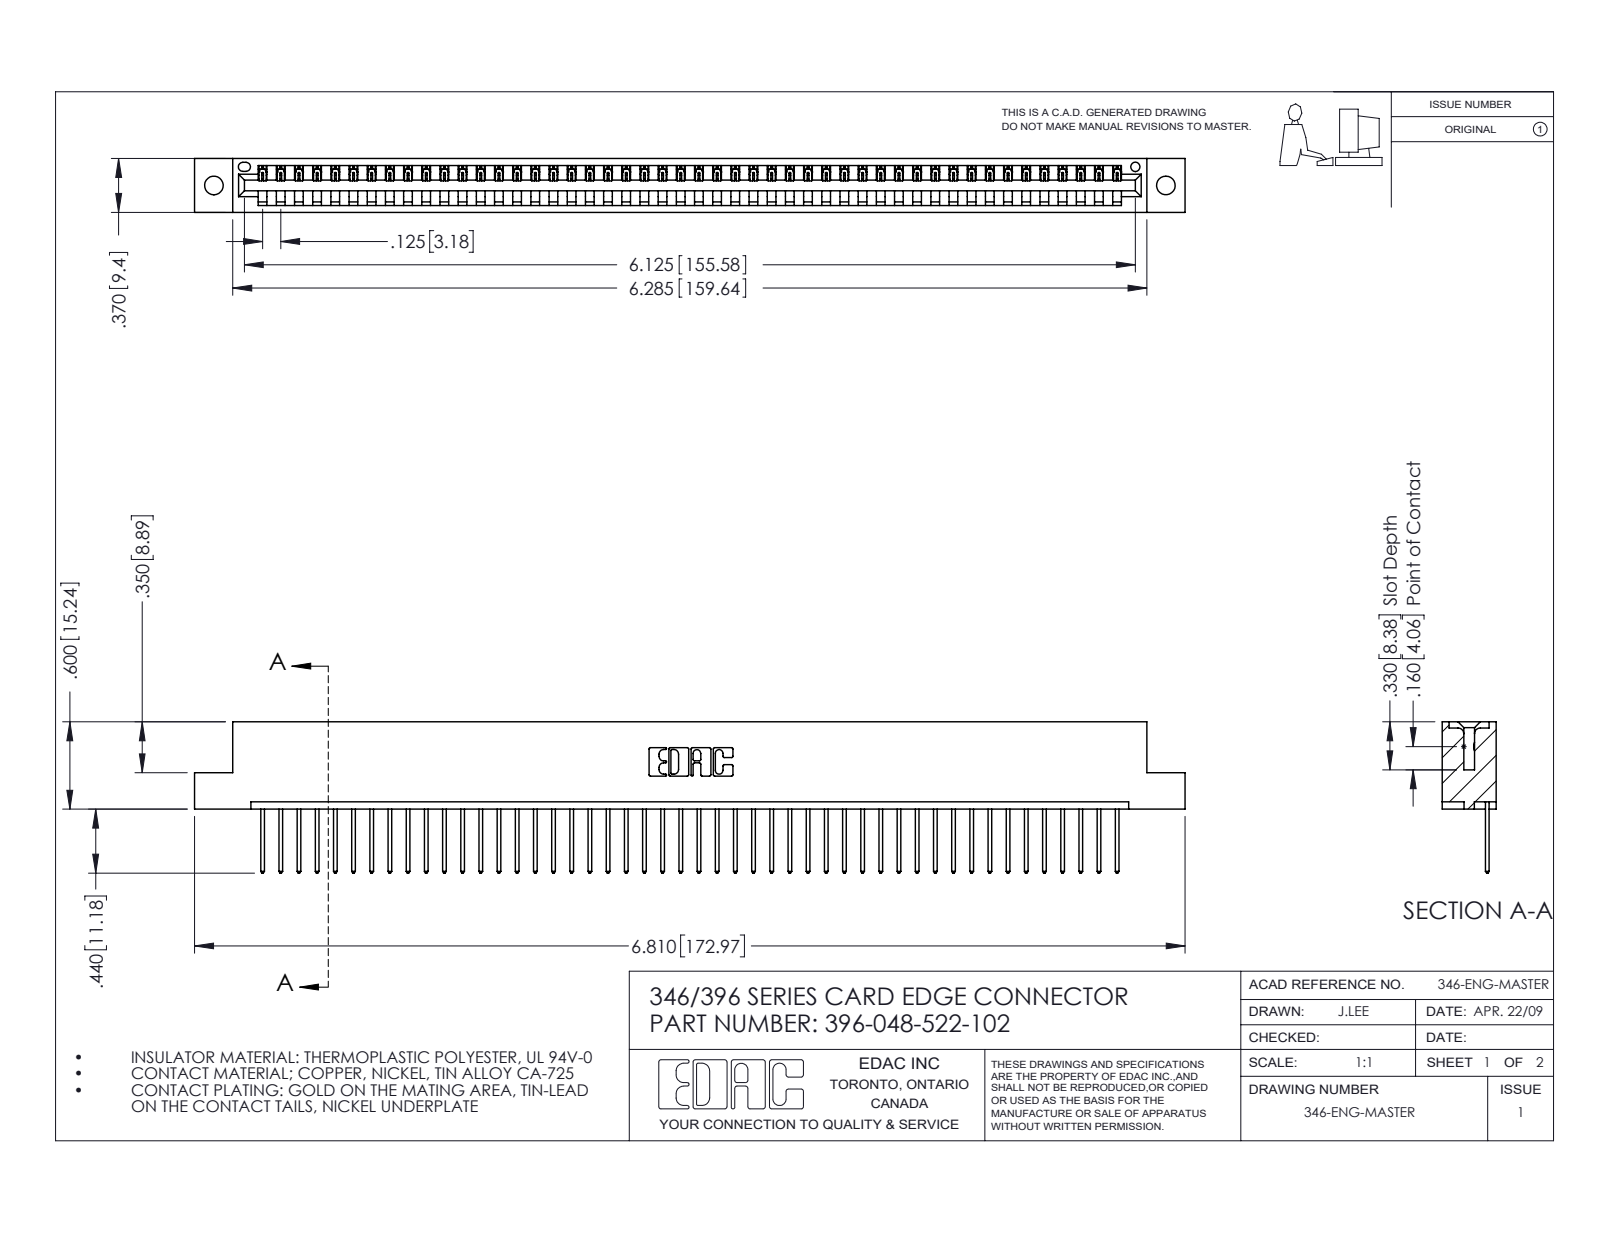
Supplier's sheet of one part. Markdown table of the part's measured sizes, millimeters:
| quantity | value |
| --- | --- |
| part name | 346 Part_Flush Mounting Lugs - 0.128 Dia; 396-048-522-102; 345-292-001_345-293-122 |
| STEP written by | SolidWorks 2016 (CONFIG_CONTROL_DESIGN) |
| units | millimeters |
| bodies | 49 solids, 2906 faces (1996 planar, 910 cylindrical, 0 other) |
| overall size | 173 × 26.4 × 9.4 |
| volume | 16 570 mm³ |
| surface area | 20 680 mm² |
| round holes (diameter × count) | 3.3 × 2, 1.6 × 1 |
| partial cylindrical surfaces (radius × count) | 0.2 × 96, 0.3 × 96, 0.3 × 22, 0.2 × 6, 0.8 × 6, 0.7 × 3, 0.8 × 2, 1 × 2 |
| main face-to-face distances | 1.2, 8.2, 9.4, 6.4, 1.8, 7.6, 0.6, 3.8, 5.6, 2.5 |
| hole center spacings | 6.2, 160.9, 166.2 |
